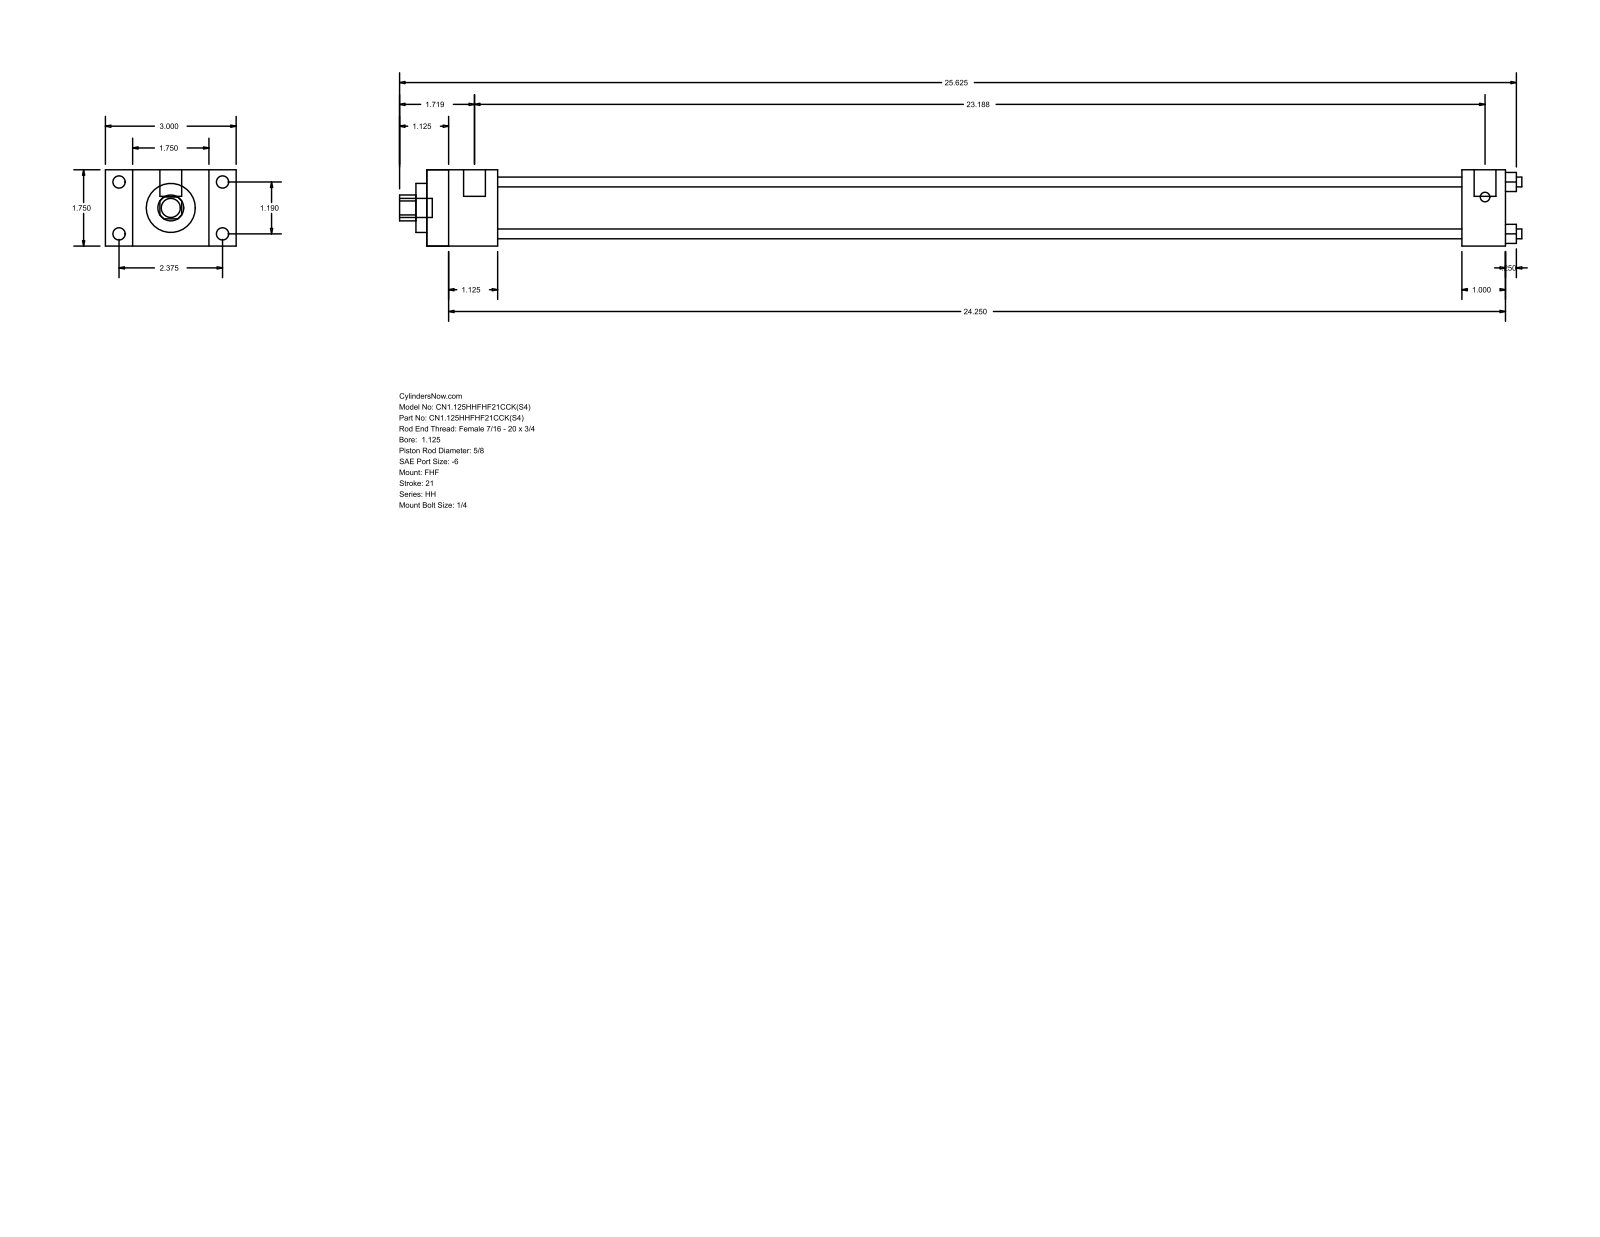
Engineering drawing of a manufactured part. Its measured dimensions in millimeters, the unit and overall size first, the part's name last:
Units: millimetres
Overall size (bounding box): 654.05 × 76.2 × 44.45
Round holes (diameter × count): ⌀5.71 ×4, ⌀15.88 ×1, ⌀28.57 ×1, ⌀34.92 ×1
Round bosses / shafts (diameter × count): ⌀7.14 ×4, ⌀5.56 ×4, ⌀12.7 ×2, ⌀11.11 ×1
Partial cylindrical surfaces — rounded edges, fillets, slot ends (radius × count): R7.54 ×1
Main face-to-face distances: 44.46, 15.87, 60.33, 41.27, 76.2, 628.64, 587.37, 603.24, 561.97, 25.4
Hole centre spacings: 21.37, 30.22, 42.74
Bodies: 0 solids, 88 faces (60 planar, 28 cylindrical, 0 other)
Part name (STEP PRODUCT): HH_FHF__0112_0.625
STEP written by: GSSL Pune (CONFIG_CONTROL_DESIGN)
